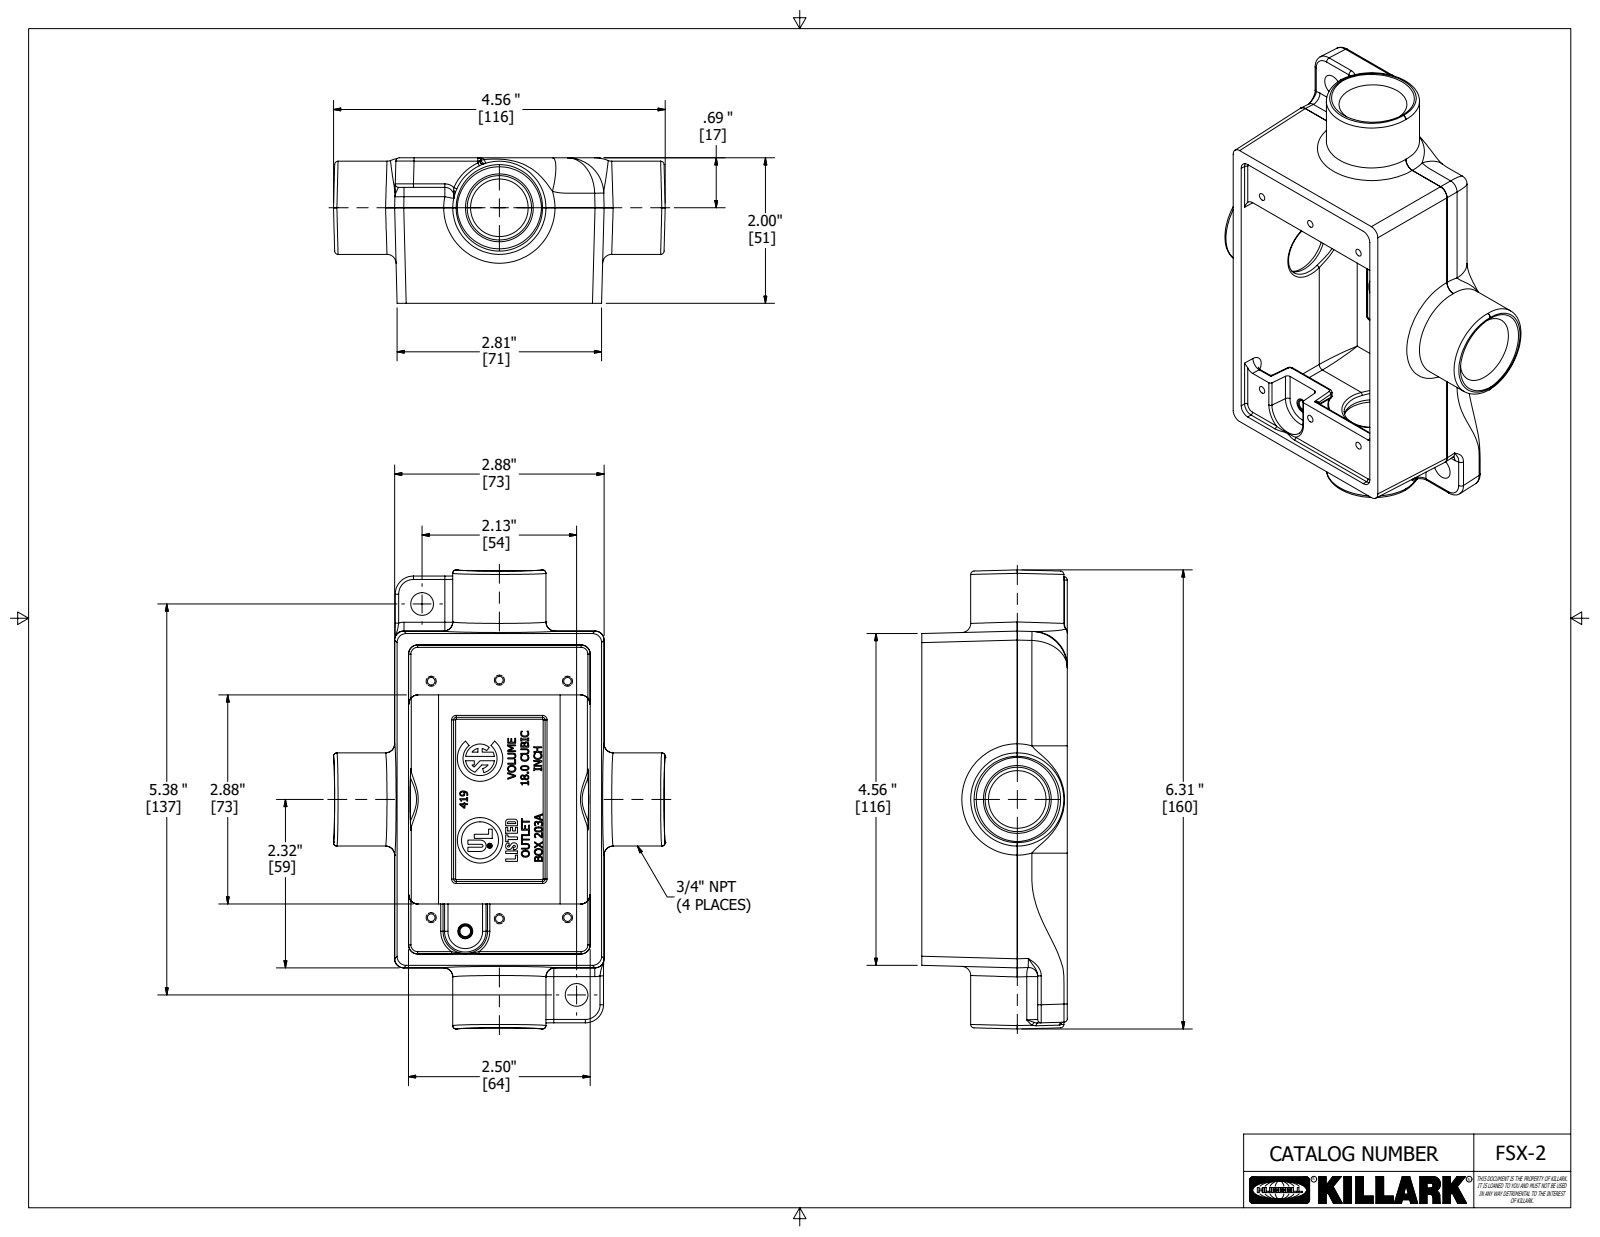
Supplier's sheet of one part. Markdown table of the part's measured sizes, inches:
| quantity | value |
| --- | --- |
| part name | 23864-3 |
| STEP written by | Autodesk Inventor 2020 (AUTOMOTIVE_DESIGN) |
| units | inches |
| bodies | 1 solid, 1186 faces (570 planar, 172 cylindrical, 444 other) |
| overall size | 6.312 × 4.562 × 2.075 |
| volume | 10.08 in³ |
| surface area | 105.5 in² |
| round holes (diameter × count) | 0.104 × 6, 0.792 × 2, 0.069 × 1, 0.145 × 1, 0.625 × 1 |
| round bosses / shafts (diameter × count) | 1.281 × 2, 0.509 × 1, 0.058 × 1 |
| partial cylindrical surfaces (radius × count) | 0.031 × 33, 0.125 × 20, 0.047 × 16, 0.094 × 7, 0.062 × 5, 0.375 × 4, 0.013 × 2, 0.014 × 2 |
| main face-to-face distances | 2.656, 0.156, 1.75, 4.406, 0.031, 1.719, 1.594, 1.906, 0.25, 0.187 |
| hole center spacings | 0.937, 3.397, 1.875, 3.25, 3.752, 0.153, 0.5, 0.505 |
